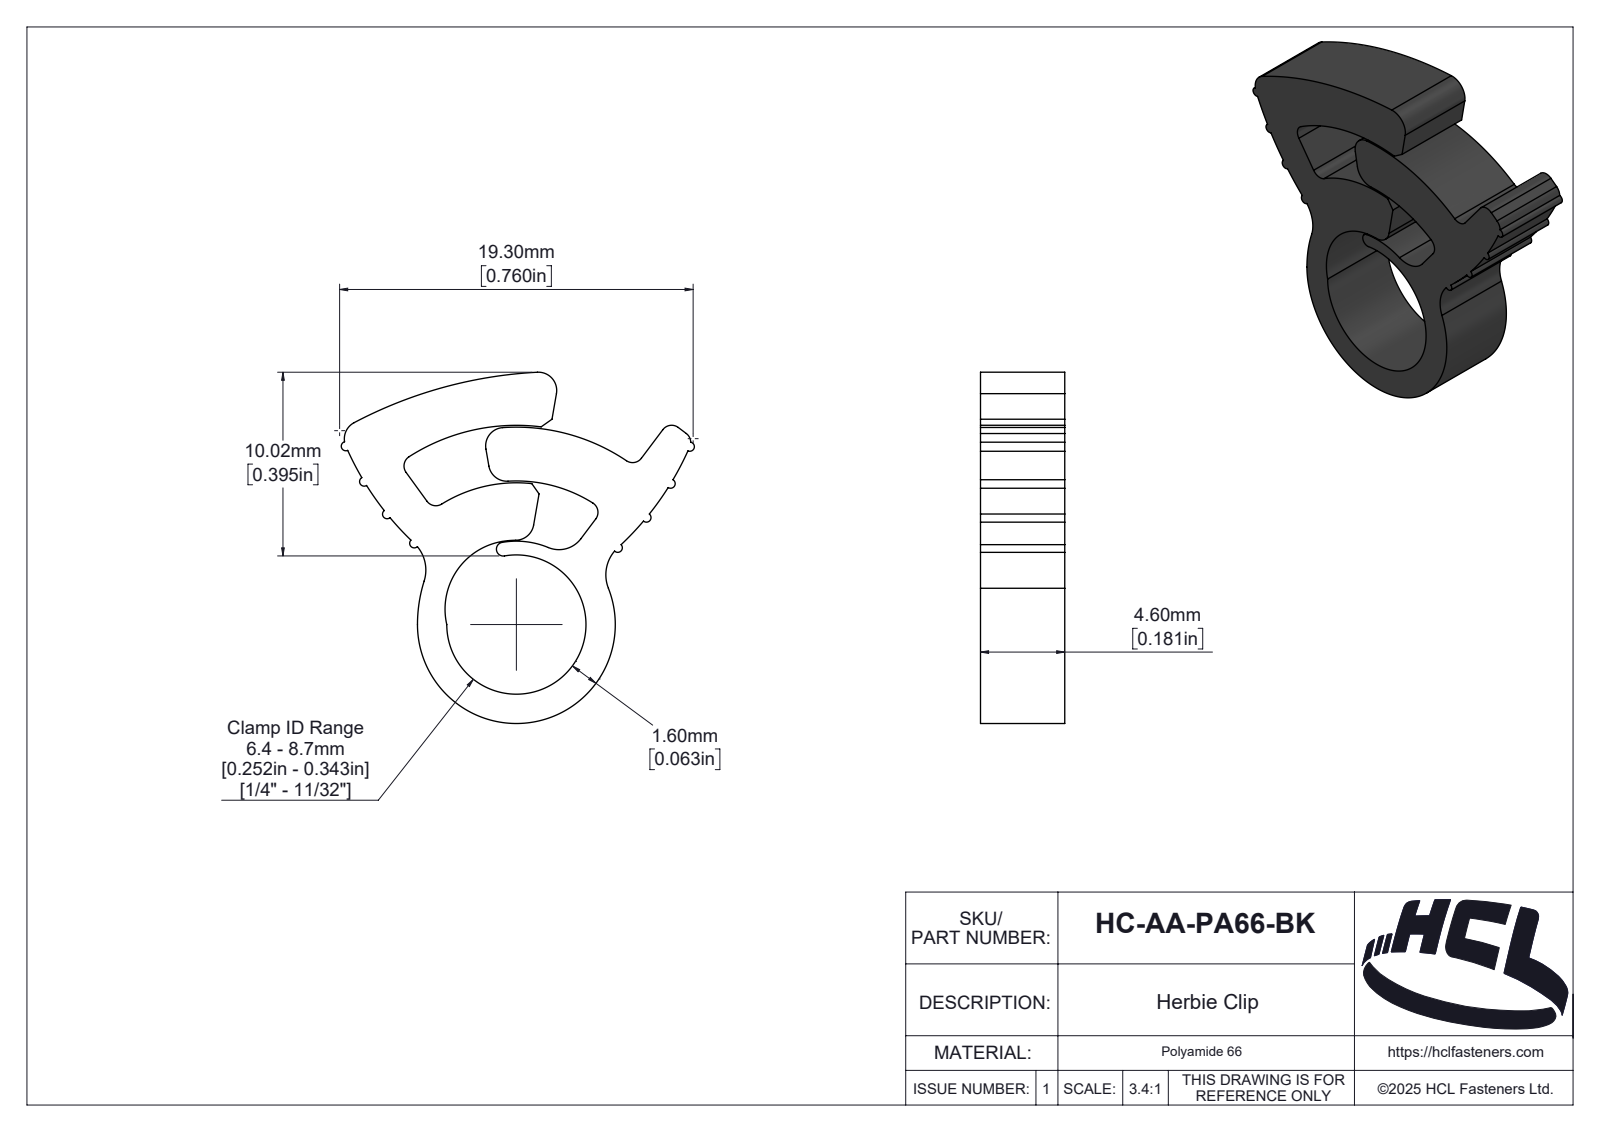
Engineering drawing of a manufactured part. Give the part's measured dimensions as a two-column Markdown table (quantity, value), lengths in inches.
| quantity | value |
| --- | --- |
| part name | HC-AA-PA66-BK |
| STEP written by | SolidWorks 2025 (AUTOMOTIVE_DESIGN) |
| units | inches |
| bodies | 1 solid, 162 faces (13 planar, 100 cylindrical, 49 other) |
| overall size | 0.759 × 0.755 × 0.181 |
| volume | 0.039 in³ |
| surface area | 1.38 in² |
| partial cylindrical surfaces (radius × count) | 0.01 × 8, 0.024 × 6, 0.039 × 5, 0.079 × 2, 0.007 × 1, 0.015 × 1, 0.026 × 1, 0.033 × 1 |
| main face-to-face distances | 0.181 |
